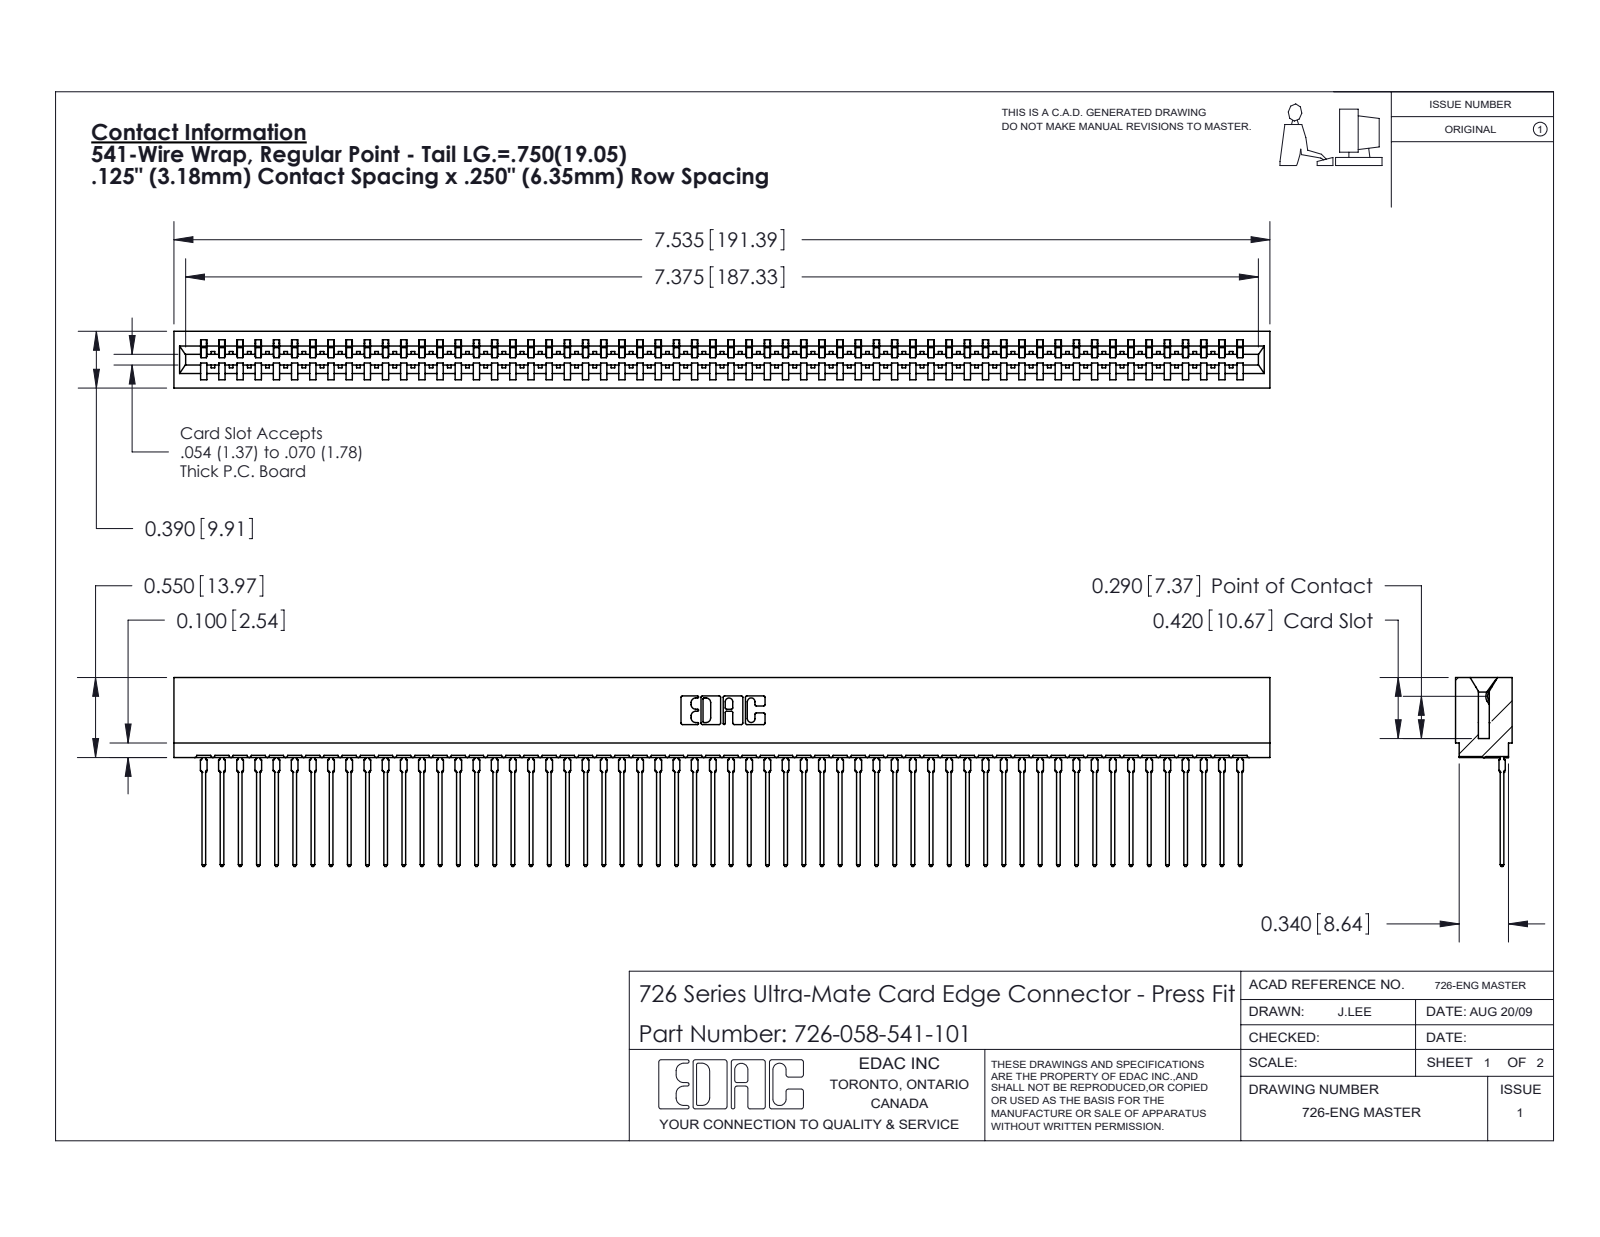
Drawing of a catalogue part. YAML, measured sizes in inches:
part_name: "726-058-541-101; 746-292-001_541; 726 Part_.515 Slot Depth - 01"
step_written_by: "SolidWorks 2020 (CONFIG_CONTROL_DESIGN)"
units: inches
bodies: {solids: 59, faces: 6361, planar: 3709, cylindrical: 1144, other: 1508}
overall_size: [7.535, 1.299, 0.39]
volume: 1.054
surface_area: 43.38
partial_cylinders:
  - {radius: 0.021, count: 116}
  - {radius: 0.015, count: 59}
  - {radius: 0.01, count: 22}
  - {radius: 0.007, count: 6}
  - {radius: 0.031, count: 6}
  - {radius: 0.005, count: 4}
  - {radius: 0.011, count: 4}
  - {radius: 0.026, count: 3}
face_to_face_distances: [0.057, 0.333, 0.39, 0.025, 0.307, 0.25, 0.083, 0.275, 0.365, 0.032]
